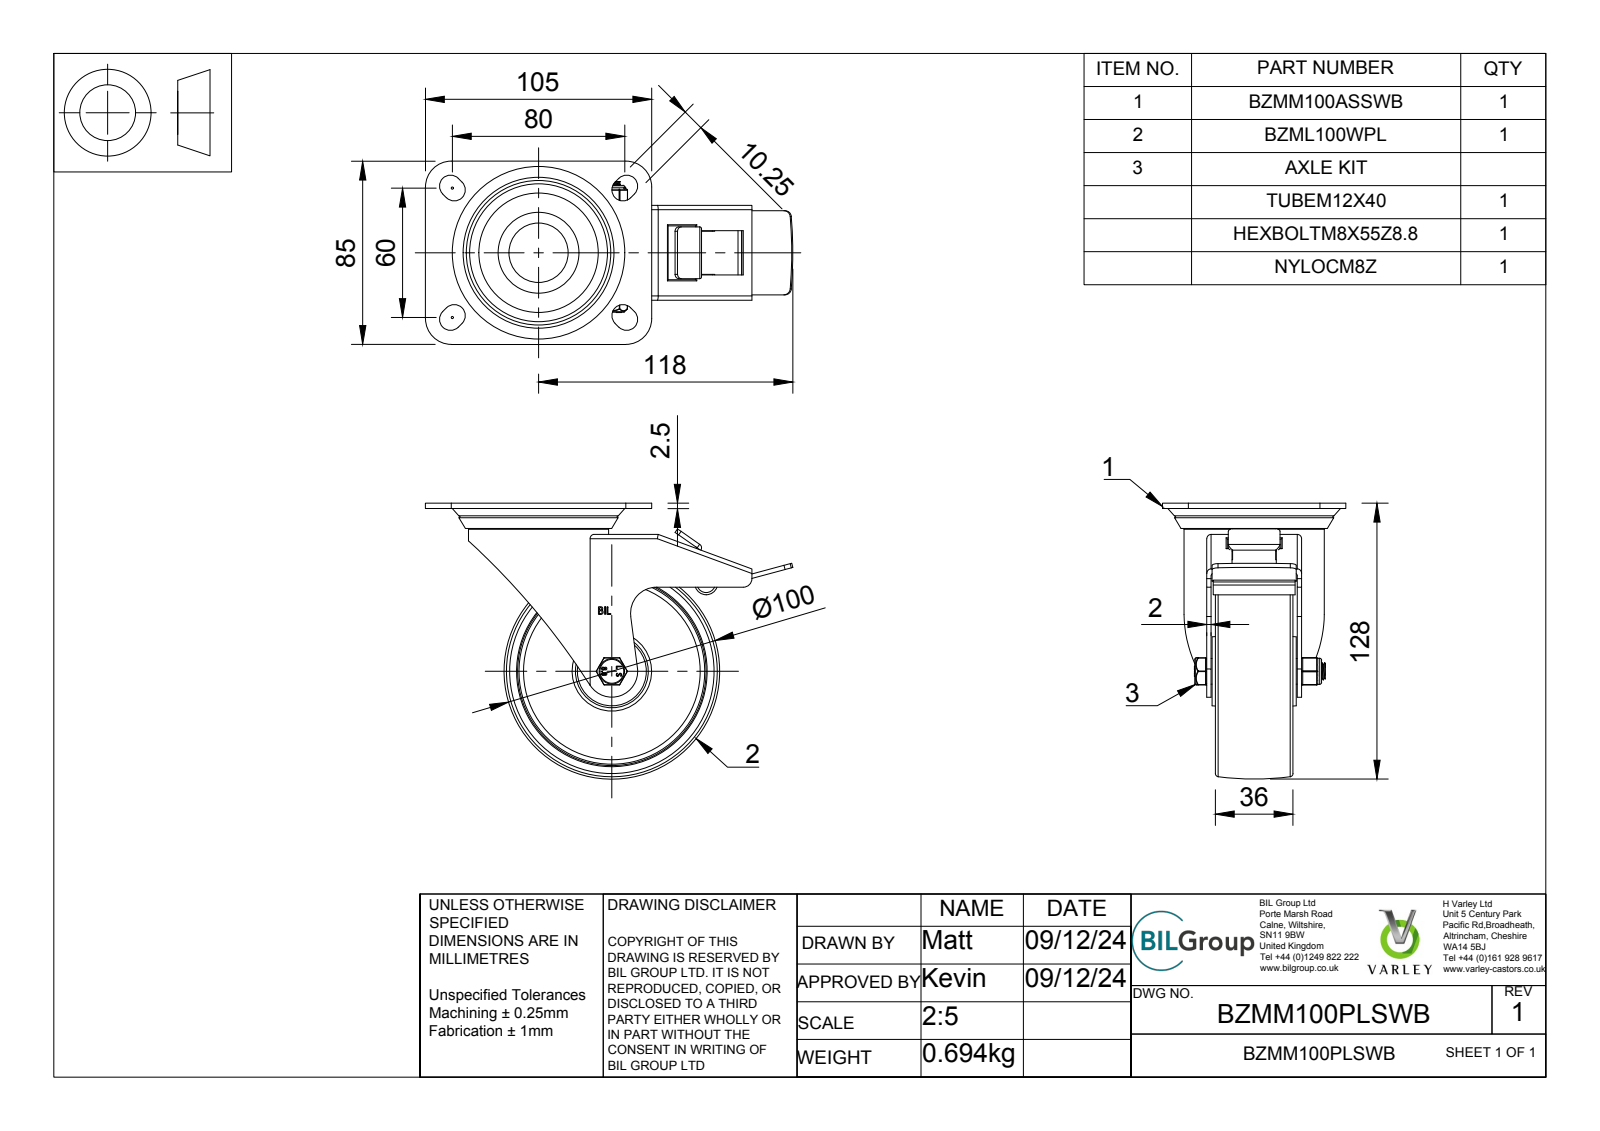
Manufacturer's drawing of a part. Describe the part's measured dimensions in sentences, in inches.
The part is named "BZMM100PLSWB v3; BZMM100ASSWB v1; ZINC PLATED, PRESSED STEEL TOP PLATE; ZINC PLATED, PRESSED STEEL TOP PLATE Geometry (+7 more)". Its 3-D file was written by "Autodesk Translation Framework v13.20.0.188 (AP242_MANAGED_MODEL_BASED_3D_ENGINEERING_MIM_LF)". It is 34 solids with 556 faces: 279 planar, 157 cylindrical and 120 other. Overall it measures 6.713 by 5.039 by 3.346 inches. Its volume is 11.99 cubic inches and its surface area 175.3 square inches. Round holes: 2 of diameter 0.026, 1 of diameter 0.315, 1 of diameter 0.323, 1 of diameter 0.331, 1 of diameter 0.339, 1 of diameter 0.48, 1 of diameter 1.083, 1 of diameter 2.205, 1 of diameter 2.402. Round bosses or shafts: 1 of diameter 2.559, 1 of diameter 1.24, 1 of diameter 0.476, 1 of diameter 0.469, 1 of diameter 0.453, 1 of diameter 0.31, 1 of diameter 0.254. Partial cylindrical surfaces (rounded edges, fillets, slot ends): 22 of radius 0.02, 12 of radius 0.01, 9 of radius 0.079, 8 of radius 0.202, 6 of radius 0.039, 5 of radius 0.472, 4 of radius 0.013, 4 of radius 0.025. The main face-to-face distances are 0.079, 0.098, 0.217, 0.974, 0.758, 0.679, 0.896, 1.654, 1.575, 0.039. The hole center spacings are 0.127, 0.098.
